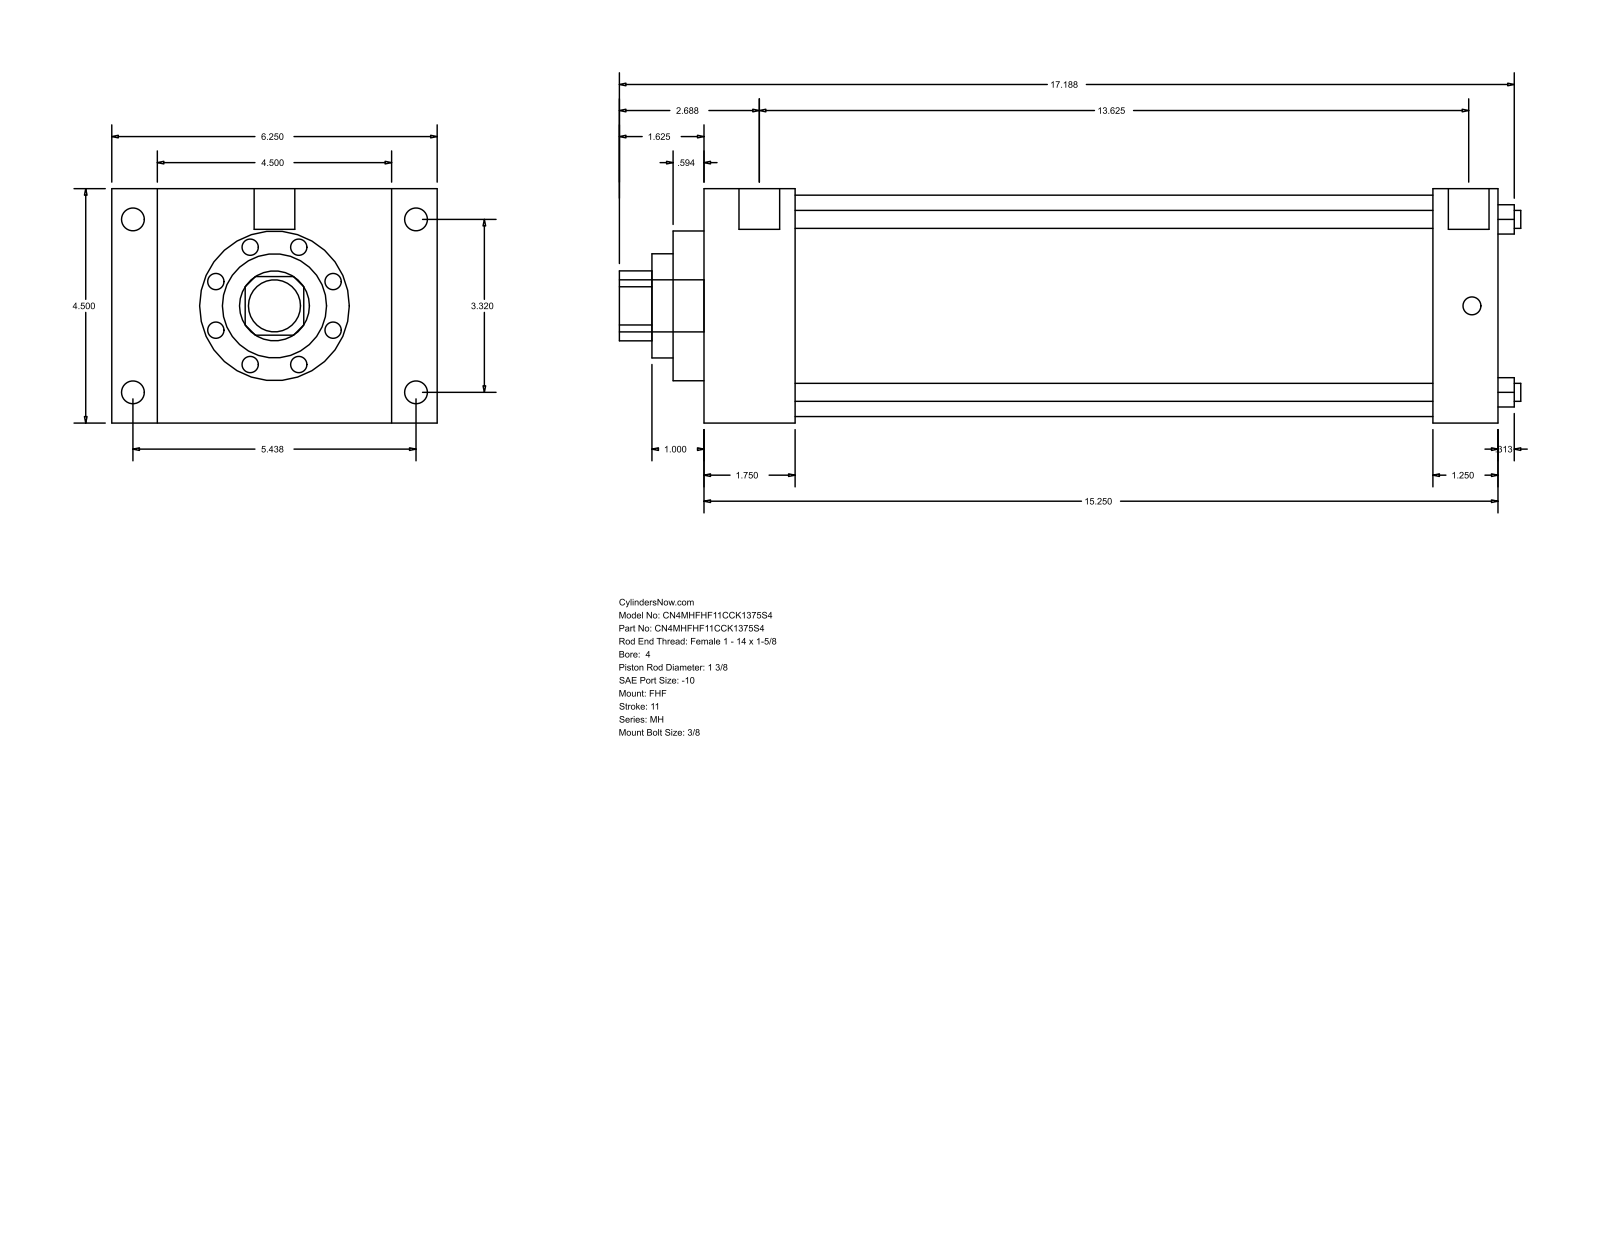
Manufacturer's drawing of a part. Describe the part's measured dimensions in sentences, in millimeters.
The part is named "MH_FHF__0400_1.375". Its 3-D file was written by "GSSL Pune (CONFIG_CONTROL_DESIGN)". It is 0 solids with 90 faces: 61 planar, 29 cylindrical and 0 other. Overall it measures 439.74 by 158.75 by 114.3 millimeters. Round holes: 4 of diameter 8.76, 1 of diameter 34.92, 1 of diameter 50.8, 1 of diameter 73.03, 1 of diameter 107.95. Round bosses or shafts: 4 of diameter 11.13, 4 of diameter 8.73, 2 of diameter 19.84, 1 of diameter 25.4. Partial cylindrical surfaces (rounded edges, fillets, slot ends): 1 of radius 17.06. The main face-to-face distances are 114.3, 387.35, 44.45, 342.9, 22.23, 136.53, 158.76, 355.61, 311.16, 31.74. The hole center spacings are 59.62, 84.32, 119.25.
